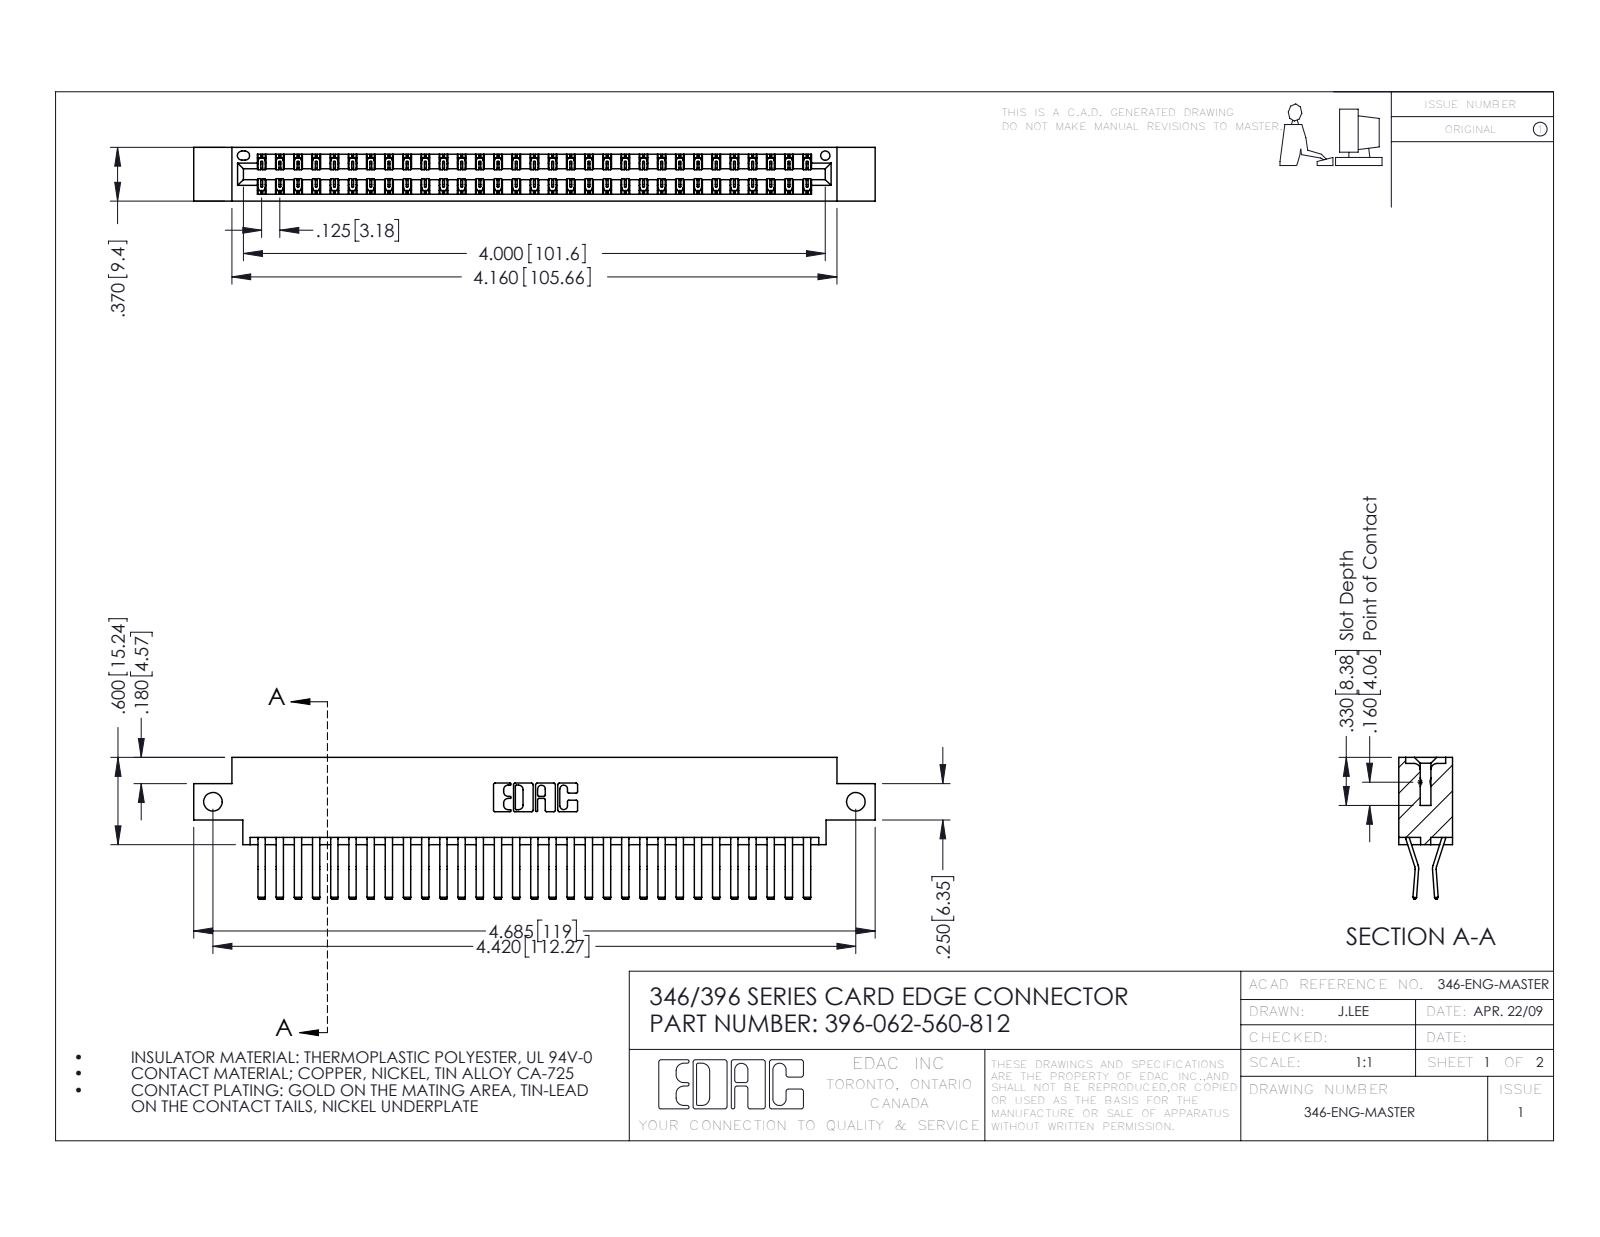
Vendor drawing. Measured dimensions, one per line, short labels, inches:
name: 345-292-001_560 Tail; 346 Part_0.170 Offset - Side Mount; 396-062-560-812
written by: SolidWorks 2016 (CONFIG_CONTROL_DESIGN)
unit: in
bodies: 63 solids, 3474 faces (2250 planar, 1224 cylindrical, 0 other)
size: 4.685 × 0.975 × 0.37
volume: 0.713 in³; area: 26.37 in²
holes: 2× ⌀0.128, 1× ⌀0.064
rounds: 93× R0.006, 22× R0.01, 6× R0.007, 6× R0.031, 3× R0.026, 2× R0.01, 2× R0.014, 2× R0.022
face distances: 0.048, 0.322, 0.37, 0.025, 0.25, 0.072, 0.298, 0.275, 0.148, 0.222
hole spacings: 4.42
